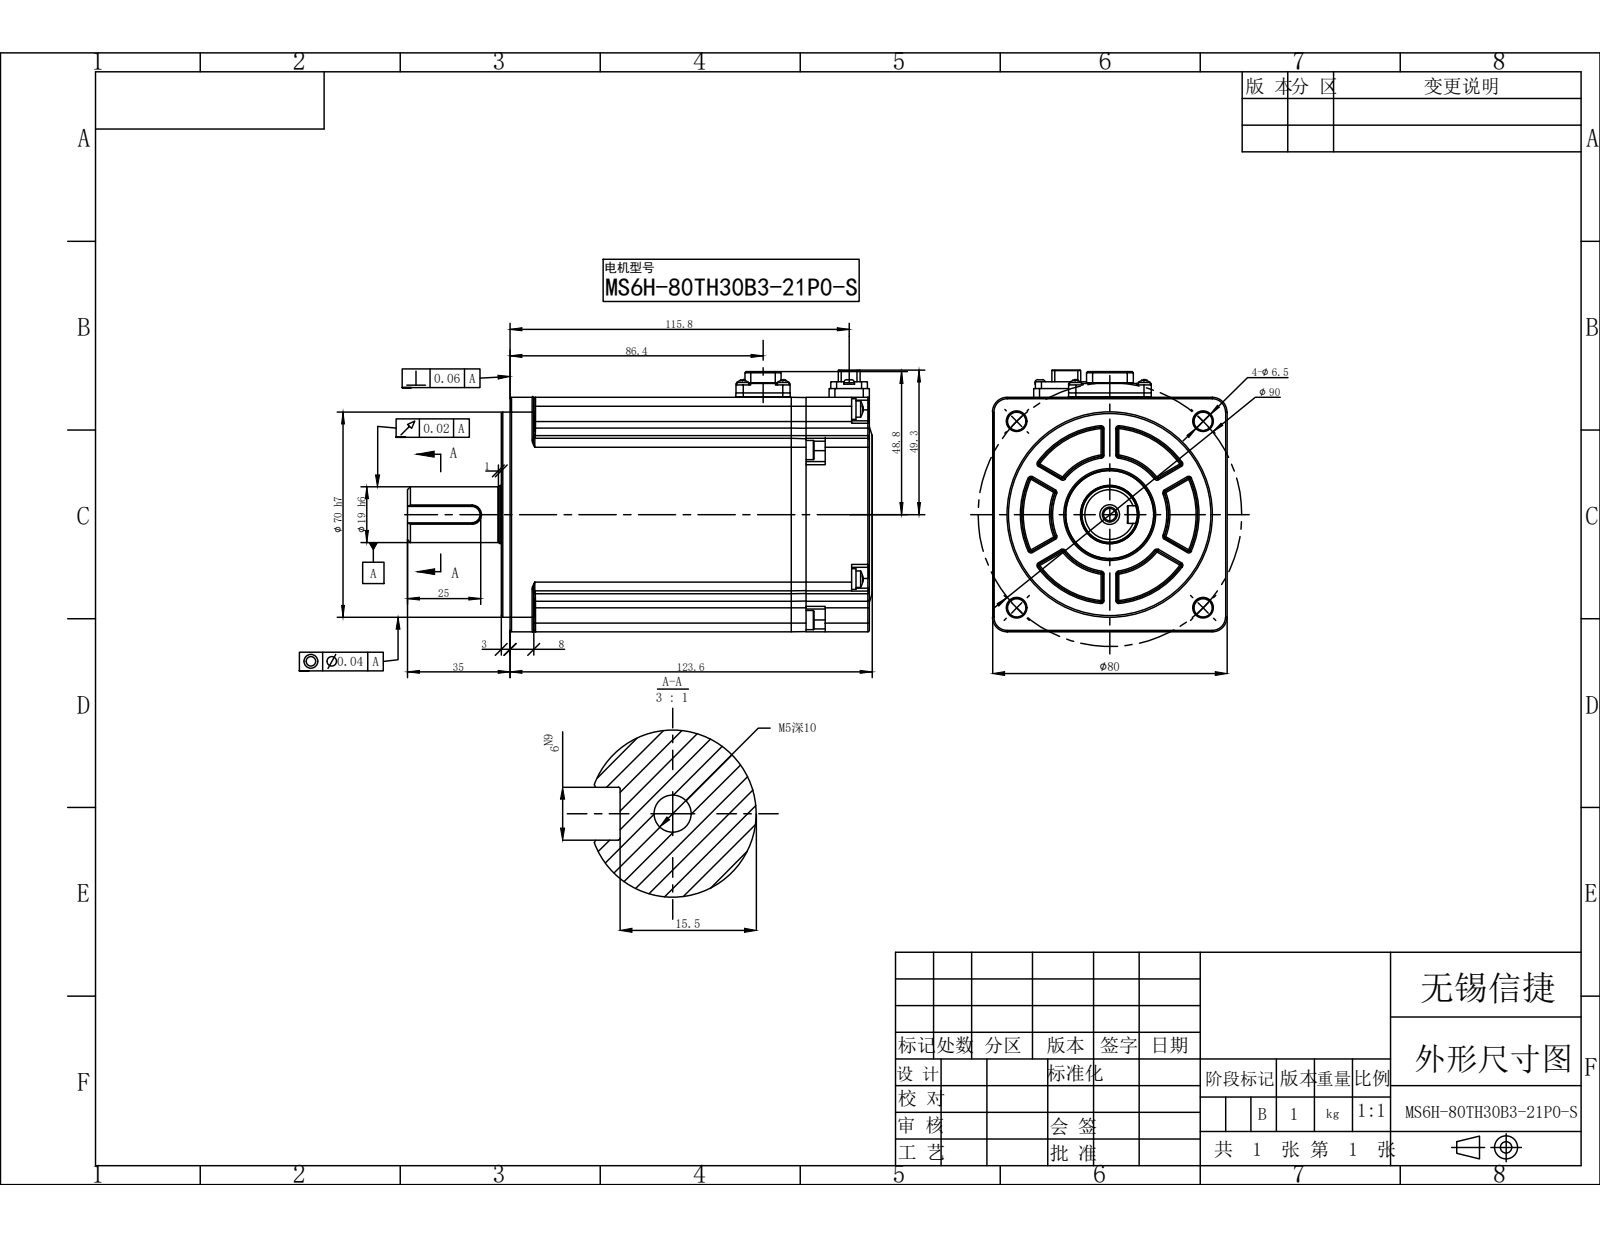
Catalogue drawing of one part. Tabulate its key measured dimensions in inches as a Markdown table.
| quantity | value |
| --- | --- |
| part name | MS6H-80TH30B3-21P0-S |
| STEP written by | SolidWorks 2022 (CONFIG_CONTROL_DESIGN) |
| units | inches |
| bodies | 0 solids, 998 faces (382 planar, 297 cylindrical, 319 other) |
| overall size | 6.244 × 3.516 × 3.15 |
| round holes (diameter × count) | 0.083 × 4, 0.063 × 2, 0.165 × 1, 0.787 × 1 |
| round bosses / shafts (diameter × count) | 0.276 × 4, 0.257 × 4, 0.22 × 4, 0.157 × 4, 0.138 × 2, 2.756 × 1, 1.181 × 1, 0.78 × 1 |
| partial cylindrical surfaces (radius × count) | 0.02 × 56, 0.008 × 23, 0.039 × 20, 0.118 × 17, 0.012 × 12, 0.079 × 12, 0.023 × 10, 0.009 × 8 |
| main face-to-face distances | 3.15, 0.551, 2.598, 0.039, 4.866, 4.827, 2.047, 1.087, 1.047, 3.78 |
| hole center spacings | 0.315, 0.654, 0.726, 0.925, 1.02, 1.097, 1.234, 1.33 |
